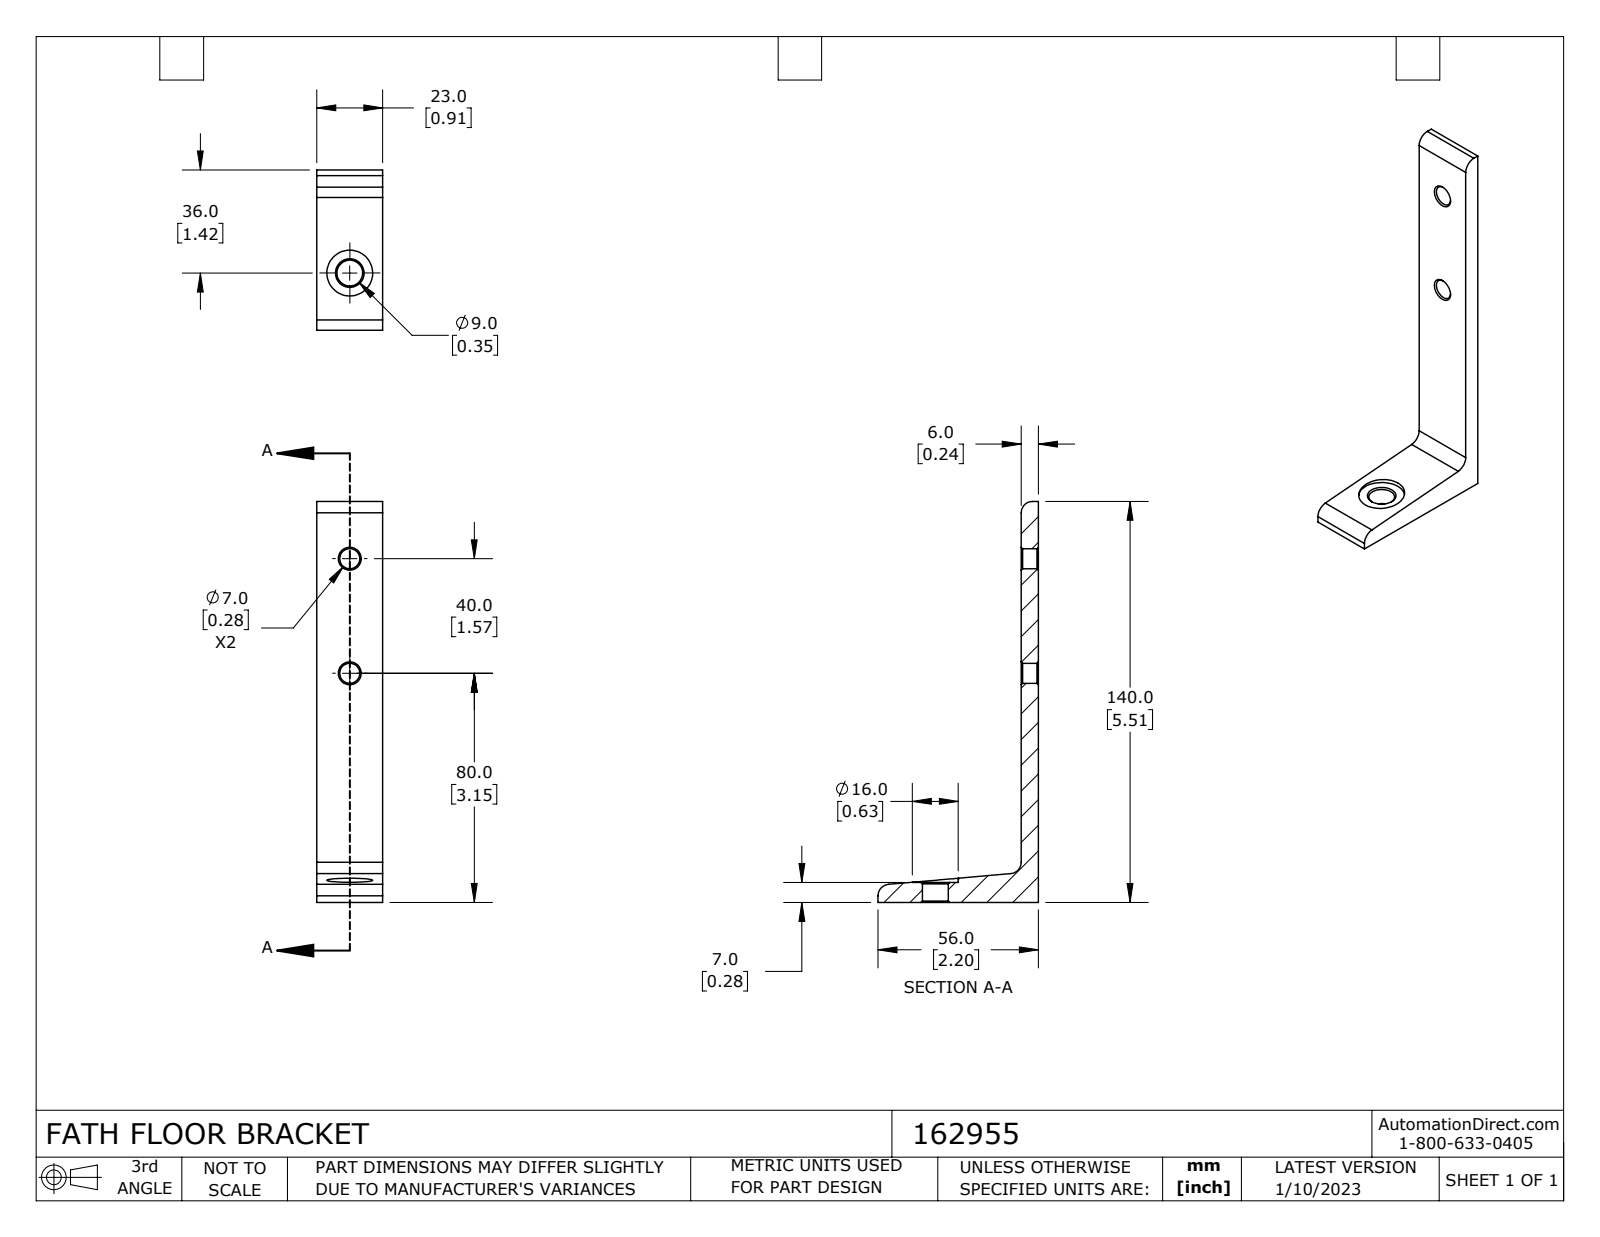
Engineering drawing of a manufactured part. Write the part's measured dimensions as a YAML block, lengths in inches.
part_name: "162955"
step_written_by: "SolidWorks 2021 (CONFIG_CONTROL_DESIGN)"
units: inches
bodies: {solids: 1, faces: 32, planar: 9, cylindrical: 11, other: 12}
overall_size: [5.512, 2.205, 0.906]
volume: 1.683
surface_area: 17.8
round_holes:
  - {diameter: 0.276, count: 2}
  - {diameter: 0.354, count: 1}
  - {diameter: 0.63, count: 1}
partial_cylinders:
  - {radius: 0.157, count: 3}
face_to_face_distances: [0.236, 0.906, 0.276, 2.205, 1.969, 5.512, 5.236]
hole_center_spacings: [1.575]
